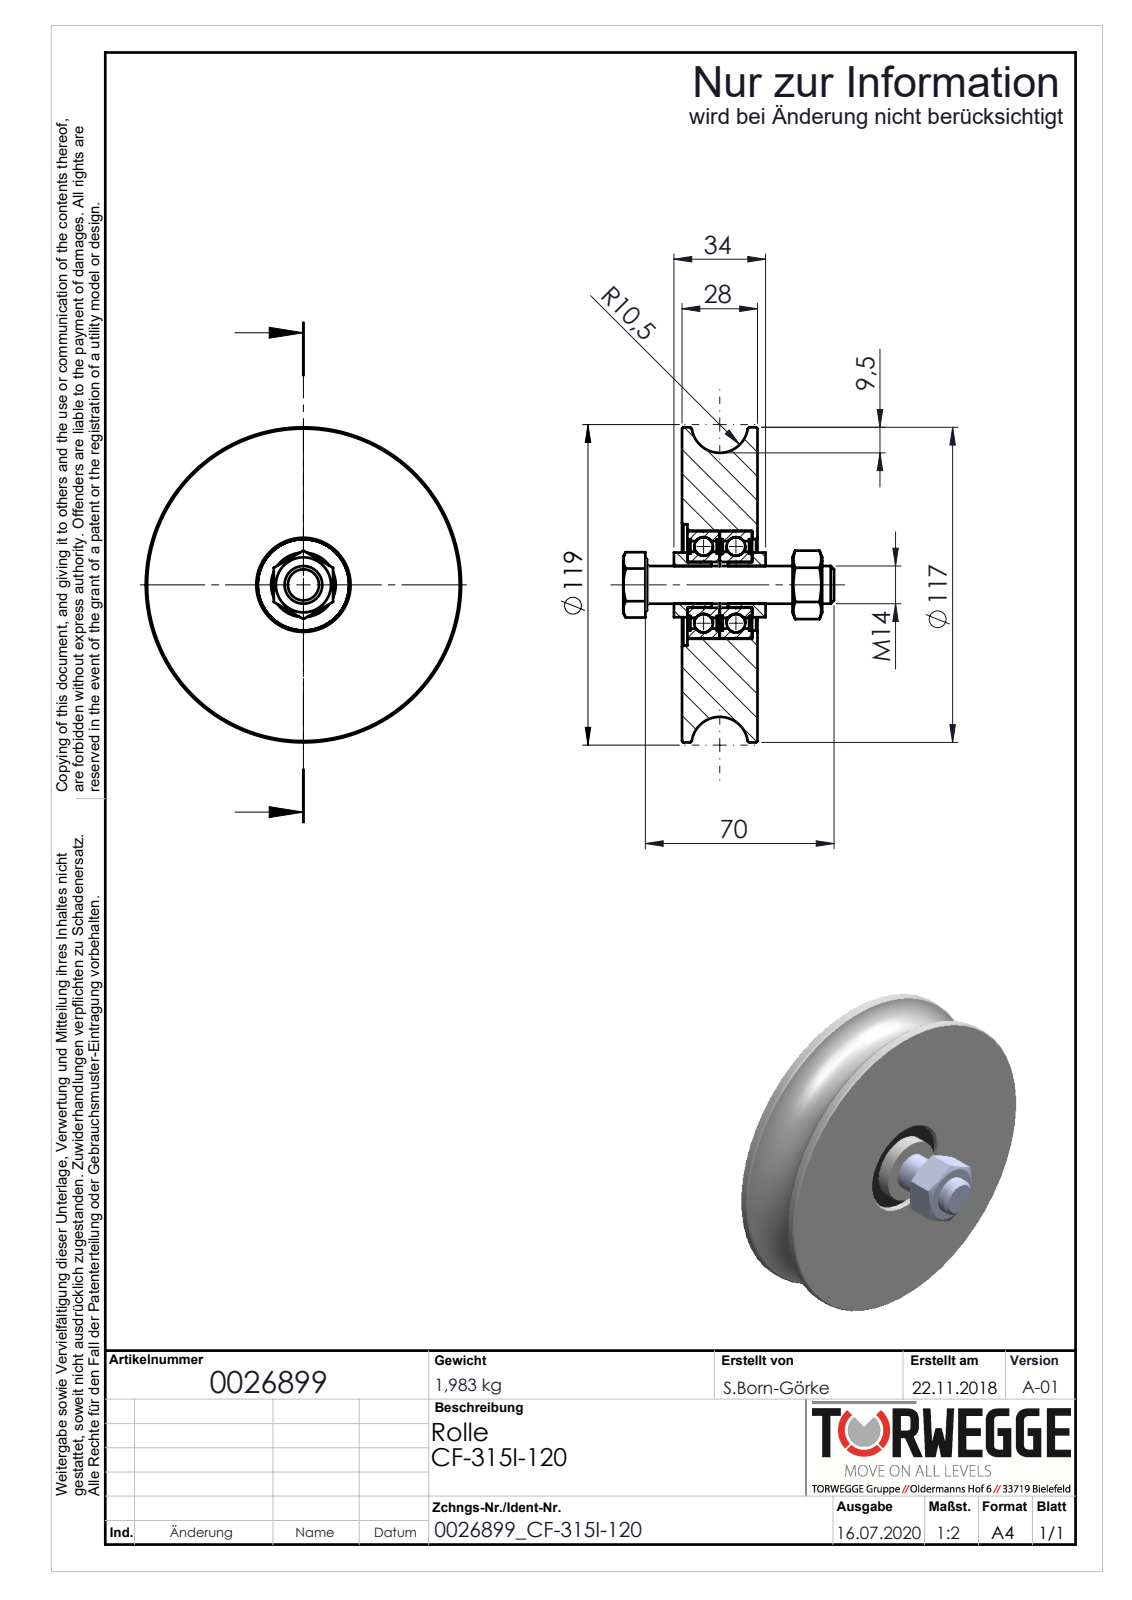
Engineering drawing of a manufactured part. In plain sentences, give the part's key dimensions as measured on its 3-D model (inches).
The part is named "0026899". Its 3-D file was written by "SolidWorks 2018 (AUTOMOTIVE_DESIGN)". It is 15 solids with 208 faces: 52 planar, 82 cylindrical and 74 other. Overall it measures 4.606 by 4.606 by 3.079 inches. Its volume is 15.64 cubic inches and its surface area 101.3 square inches. Round holes: 1 of diameter 0.466, 1 of diameter 0.551, 1 of diameter 0.669, 1 of diameter 0.909, 1 of diameter 1.28, 1 of diameter 1.335, 1 of diameter 1.339, 1 of diameter 1.772. Round bosses or shafts: 1 of diameter 4.606, 1 of diameter 1.575, 1 of diameter 0.965, 1 of diameter 0.945, 1 of diameter 0.665. The main face-to-face distances are 1.102, 0.472, 0.551, 1.024, 0.079, 0.022, 0.45, 0.945, 0.428, 0.494.
